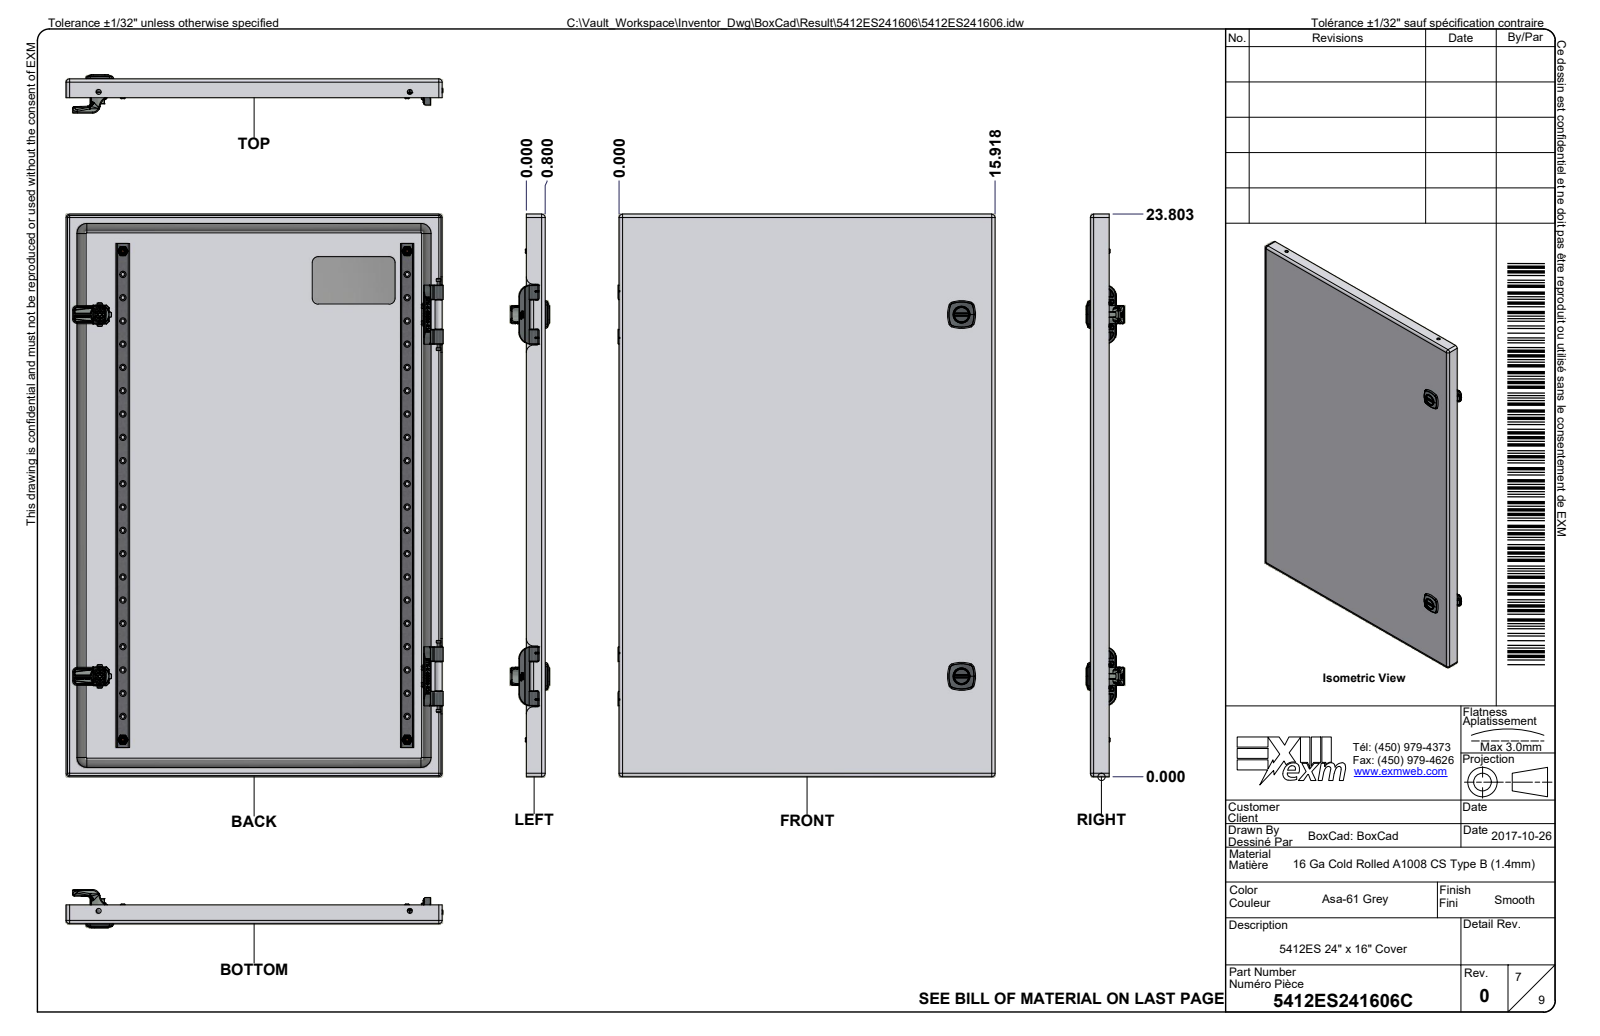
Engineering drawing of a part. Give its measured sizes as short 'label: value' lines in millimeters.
name: 5412ES241606; 5412ES241606B; 5412ES241606B-P; STK-Q-16005 (+8 more)
written by: Autodesk Inventor 2024 (AUTOMOTIVE_DESIGN)
unit: mm
bodies: 64 solids, 10070 faces (3049 planar, 2555 cylindrical, 4466 other)
size: 609.6 × 406.5 × 185.7
volume: 2 024 000 mm³; area: 2 504 000 mm²
holes: 40× ⌀4.2, 9× ⌀0.8, 8× ⌀1.1, 8× ⌀5.1, 8× ⌀8, 6× ⌀7.9, 4× ⌀4.5, 4× ⌀5, 4× ⌀6.8, 4× ⌀6.9, 4× ⌀7.4, 4× ⌀9.9
bosses: 40× ⌀6, 9× ⌀5.9, 9× ⌀0.8, 8× ⌀1, 4× ⌀18.2, 4× ⌀9.5, 4× ⌀7.9, 4× ⌀6.7
rounds: 263× R0.5, 139× R0.3, 109× R1, 94× R0.2, 50× R0.3, 32× R0.8, 30× R0.4, 24× R2.1
face distances: 1.3, 179.9, 178.5, 181.2, 23.5, 22.2, 156.3, 157.7, 26.2, 24.9
hole spacings: 50, 25, 75, 100, 388.7, 125, 150, 175
